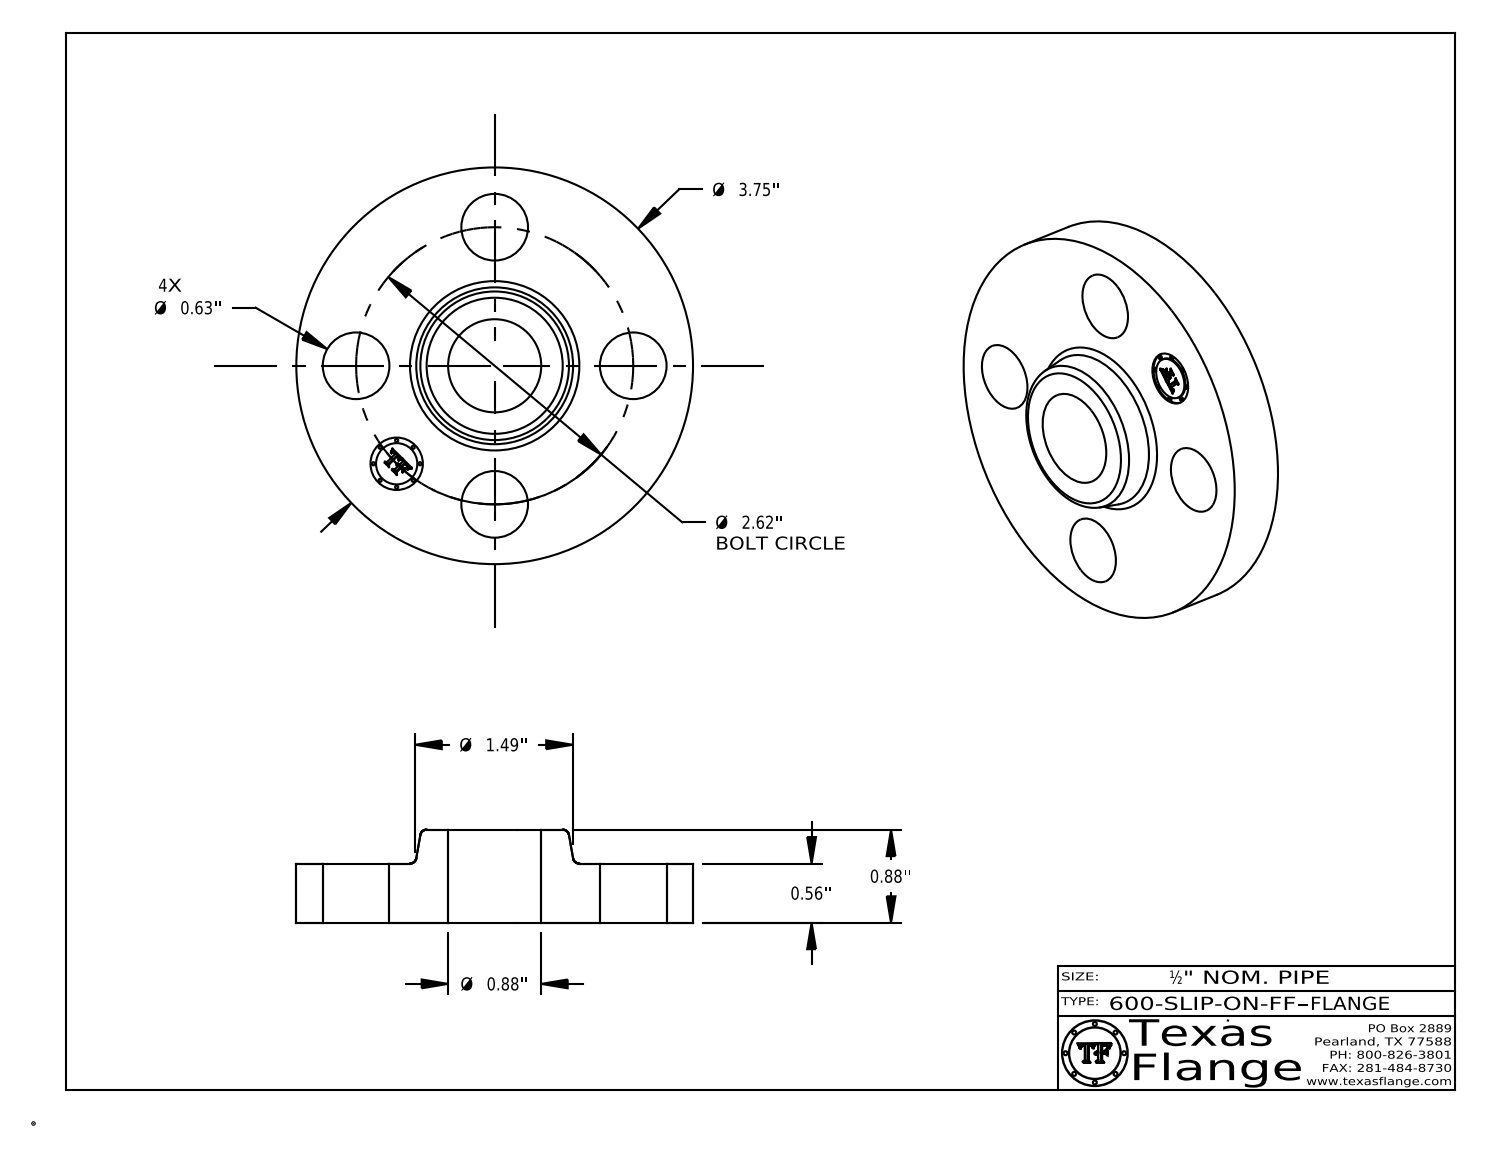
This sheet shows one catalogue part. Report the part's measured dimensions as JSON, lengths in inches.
{"part_name": "600-SLIP-ON-FF", "step_written_by": "CATIA V5 STEP AP214 (AUTOMOTIVE_DESIGN)", "units": "inches", "bodies": {"solids": 1, "faces": 406, "planar": 368, "cylindrical": 32, "other": 6}, "overall_size": [3.75, 3.75, 0.88], "volume_in3": 5.475, "surface_area_in2": 33, "round_holes": [[0.63, 4], [0.495, 1], [0.88, 1]], "round_bosses_or_shafts": [[0.03, 8], [3.75, 1], [0.39, 1]], "face_to_face_distances": [0.56, 0.88, 0.32, 0.545, 0.015, 0.335, 0.148, 0.144, 0.027, 0.096], "hole_center_spacings": [1.31, 1.852, 1.003, 2.42, 2.62, 1.31]}
